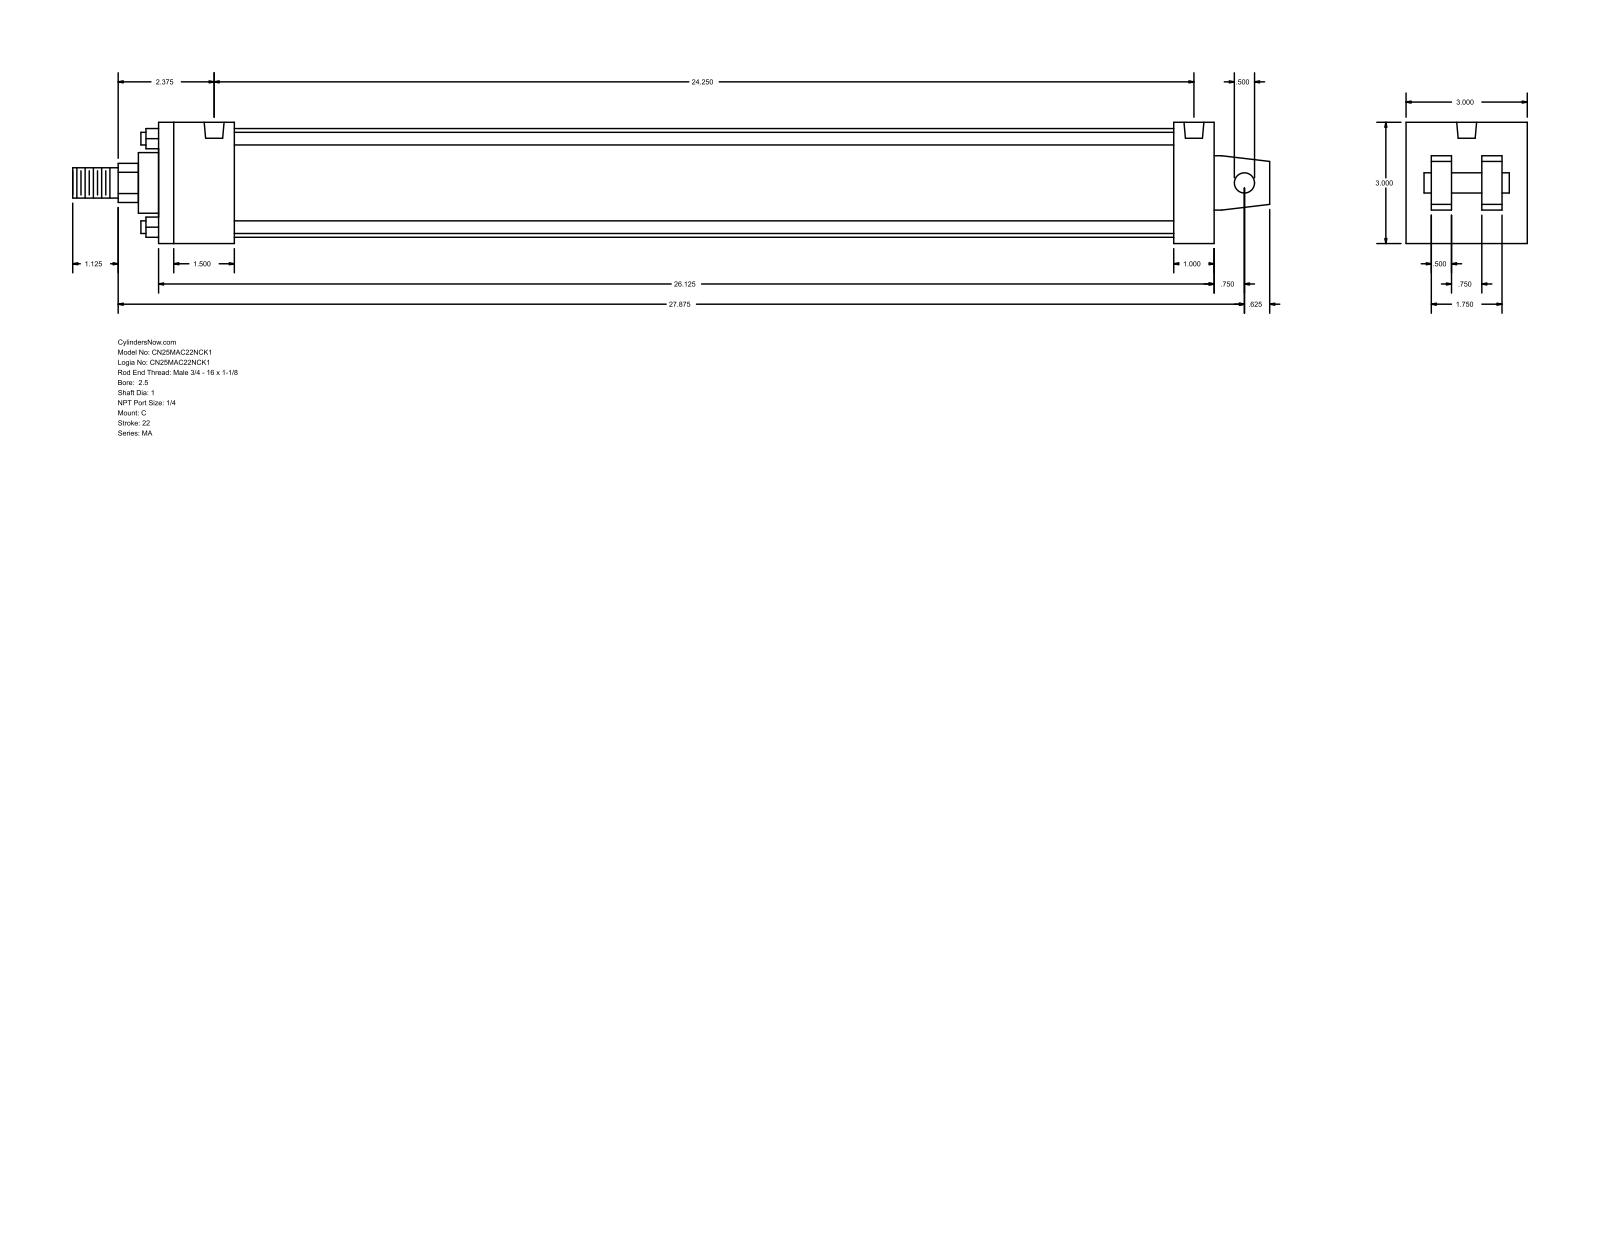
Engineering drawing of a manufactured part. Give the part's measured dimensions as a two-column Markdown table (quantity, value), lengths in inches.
| quantity | value |
| --- | --- |
| part name | MA_C__0250_1 |
| STEP written by | GSSL Pune (CONFIG_CONTROL_DESIGN) |
| units | inches |
| bodies | 0 solids, 103 faces (76 planar, 27 cylindrical, 0 other) |
| overall size | 29.625 × 3 × 3 |
| round holes (diameter × count) | 0.313 × 4, 0.492 × 2 |
| round bosses / shafts (diameter × count) | 0.313 × 4, 2.69 × 1, 1.5 × 1, 1 × 1, 0.75 × 1, 0.5 × 1 |
| partial cylindrical surfaces (radius × count) | 0.484 × 1 |
| main face-to-face distances | 3, 26.125, 1.875, 0.5, 2.375, 0.625, 1, 1.125, 25.125, 23.25 |
| hole center spacings | 24.25 |
